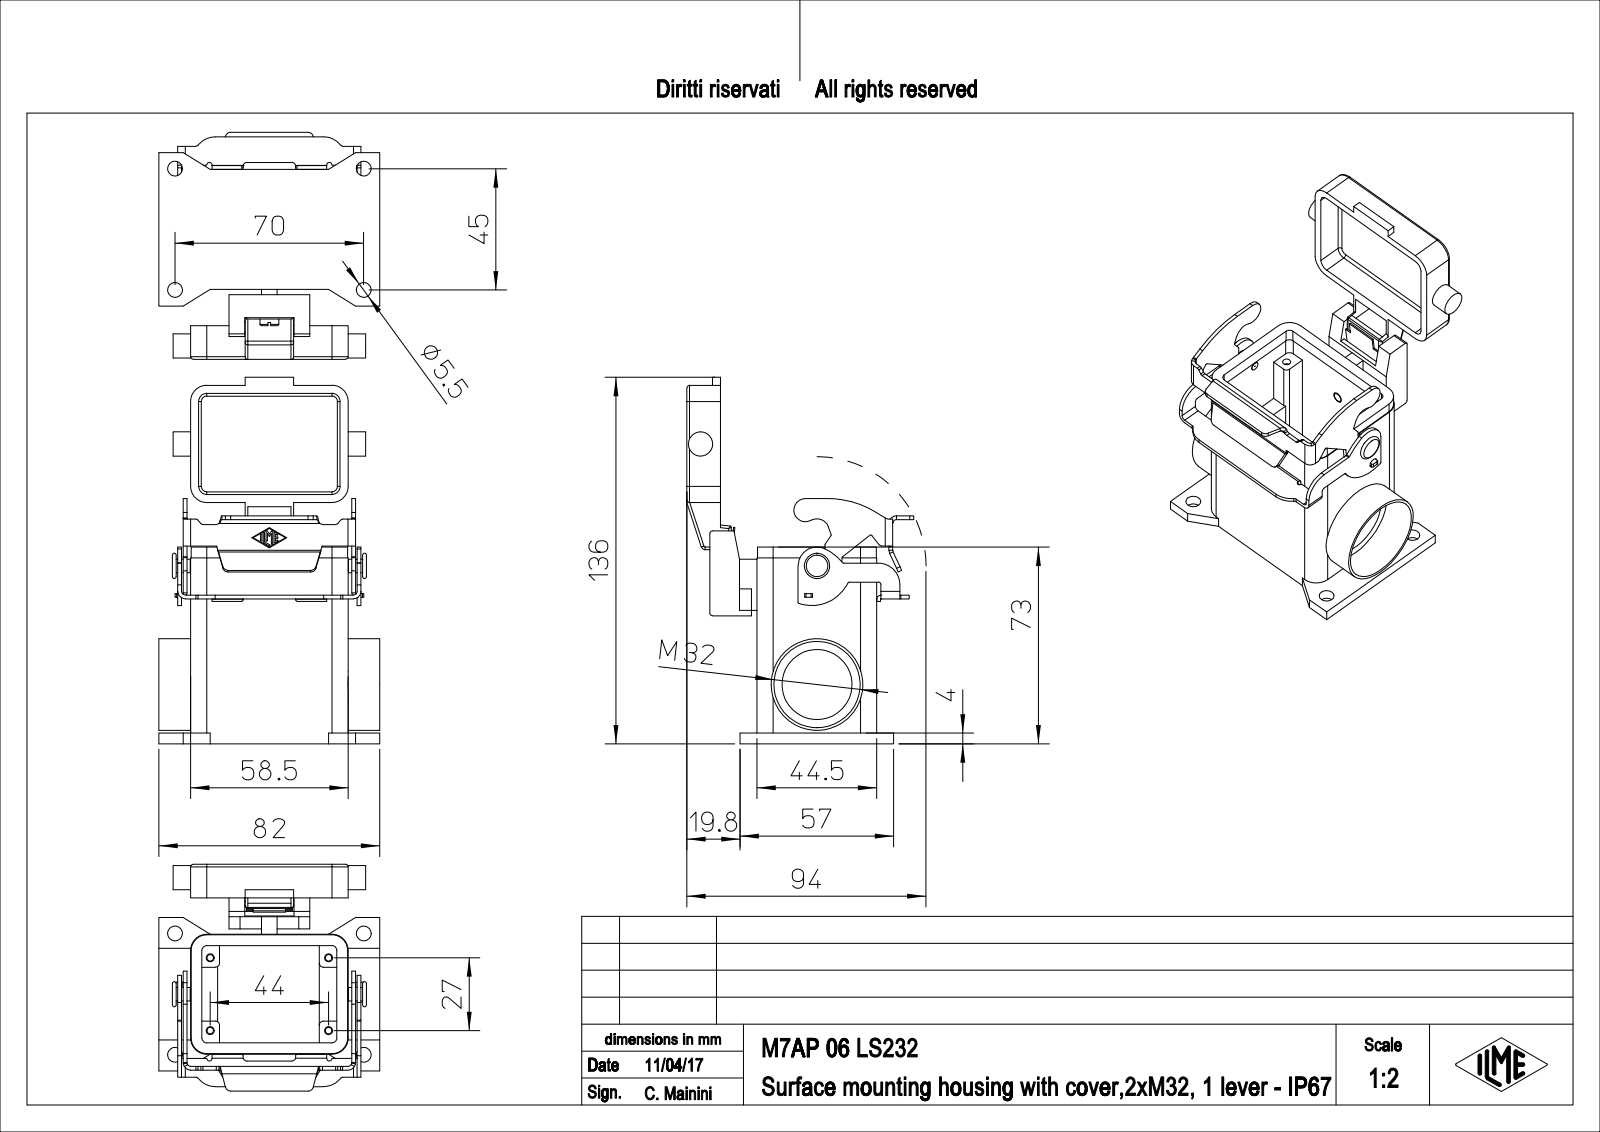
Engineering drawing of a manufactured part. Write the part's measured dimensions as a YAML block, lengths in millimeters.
part_name: "M7AP_06_LS232"
step_written_by: "PTC Creo Elements/Direct Modeling 19.0E 27-Jun-2016 (C) Parametric Technology GmbH (AUTOMOTIVE_DESIGN)"
units: millimeters
bodies: {solids: 1, faces: 546, planar: 281, cylindrical: 225, other: 40}
overall_size: [136, 84.23, 82]
volume: 106255
surface_area: 63740
round_holes:
  - {diameter: 2.46, count: 4}
  - {diameter: 3, count: 4}
  - {diameter: 5.5, count: 4}
  - {diameter: 3.5, count: 1}
  - {diameter: 4, count: 1}
  - {diameter: 26, count: 1}
  - {diameter: 32, count: 1}
round_bosses_or_shafts:
  - {diameter: 34, count: 1}
  - {diameter: 9, count: 1}
  - {diameter: 7, count: 1}
  - {diameter: 5, count: 1}
  - {diameter: 3.75, count: 1}
  - {diameter: 3.2, count: 1}
  - {diameter: 3, count: 1}
partial_cylinders:
  - {radius: 1, count: 31}
  - {radius: 0.25, count: 16}
  - {radius: 0.5, count: 13}
  - {radius: 1.5, count: 12}
  - {radius: 2, count: 9}
  - {radius: 6, count: 8}
  - {radius: 1.4, count: 6}
  - {radius: 2.8, count: 6}
face_to_face_distances: [4, 40.5, 1.4, 44.5, 26, 30, 36.5, 64, 68, 70.5]
hole_center_spacings: [15.81, 38.28, 57.71, 67.42, 27, 44, 45, 51.62]
